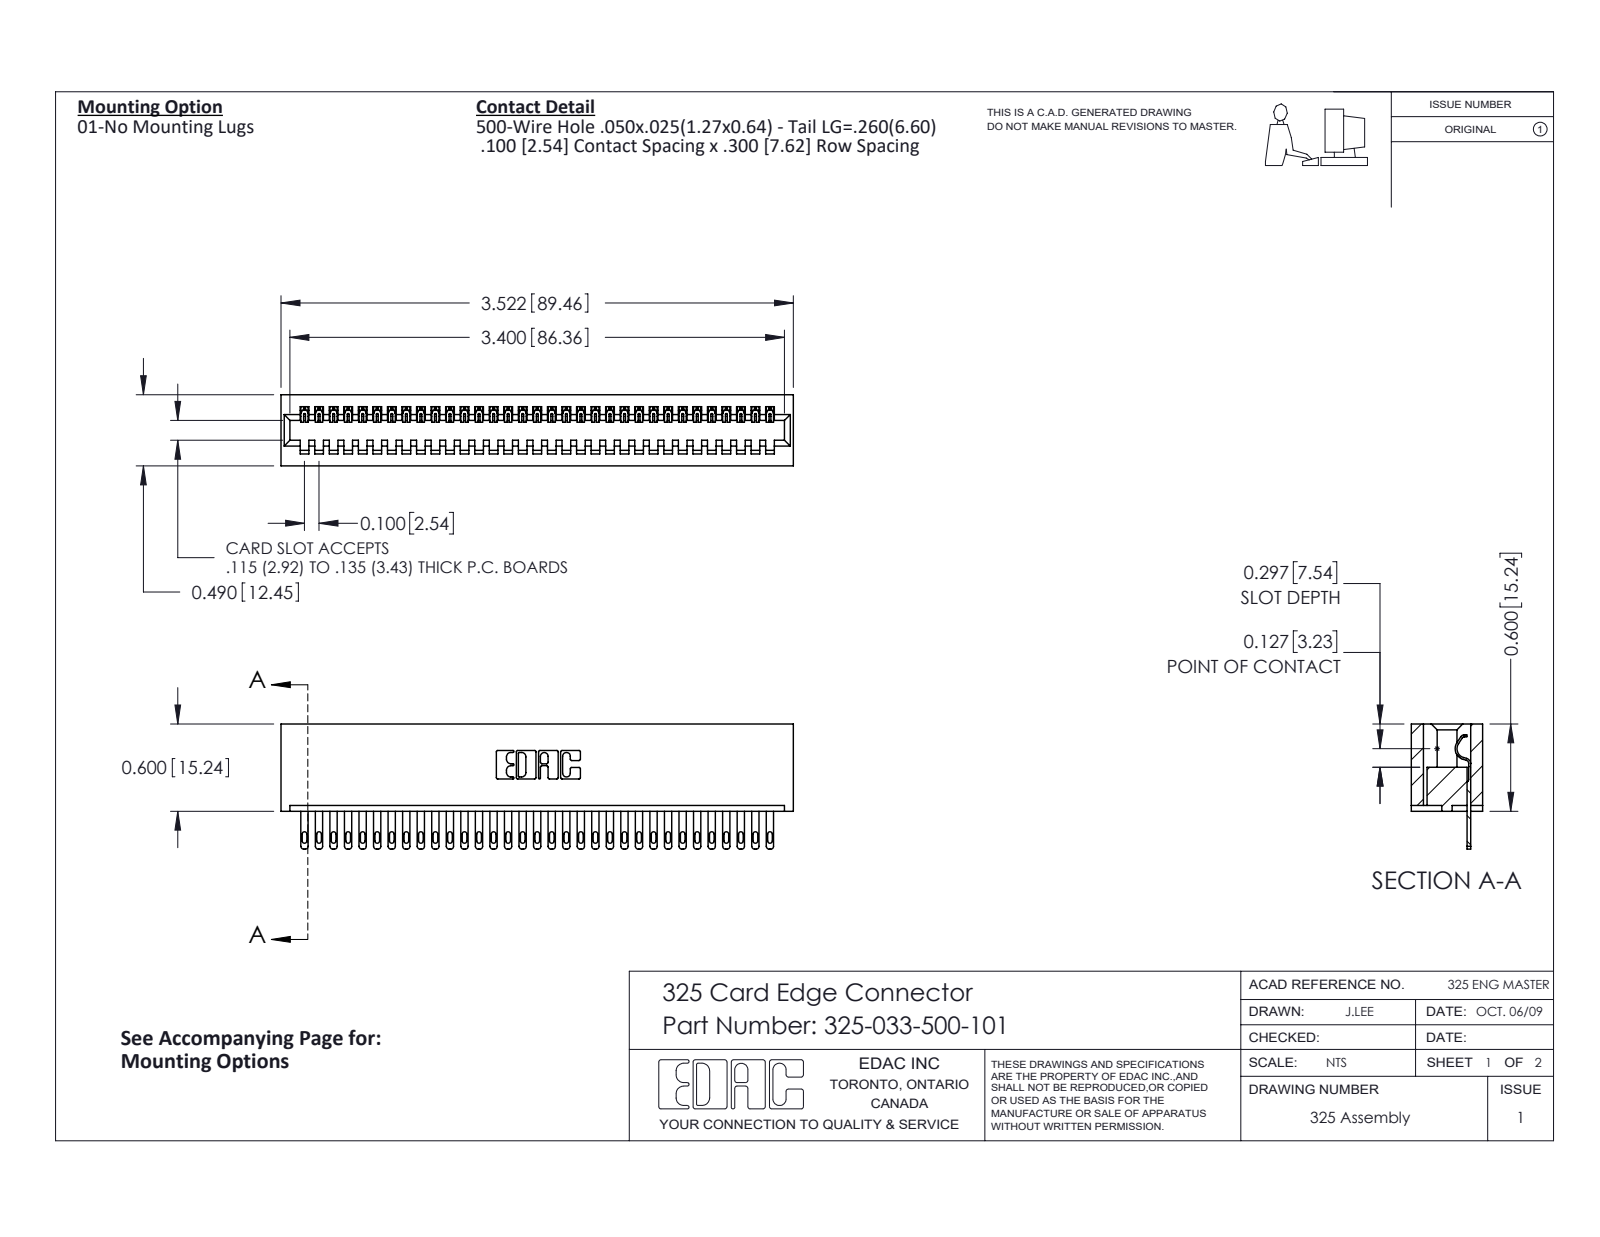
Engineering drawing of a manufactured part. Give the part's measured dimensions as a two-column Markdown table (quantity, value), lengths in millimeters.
| quantity | value |
| --- | --- |
| part name | 325-033-500-101; 325 Part_Lugless; 325-292-001_325-293-100 |
| STEP written by | SolidWorks 2016 (CONFIG_CONTROL_DESIGN) |
| units | millimeters |
| bodies | 34 solids, 1888 faces (1254 planar, 634 cylindrical, 0 other) |
| overall size | 89.5 × 21.8 × 12.4 |
| volume | 11 900 mm³ |
| surface area | 13 390 mm² |
| partial cylindrical surfaces (radius × count) | 0.2 × 66, 0.4 × 66, 0.5 × 66, 0.3 × 22, 0.2 × 6, 0.8 × 6, 0.7 × 3, 0.4 × 1 |
| main face-to-face distances | 2.1, 10.3, 7.6, 12.4, 2.7, 9.7, 0.6, 8.3, 14.2, 6.7 |
